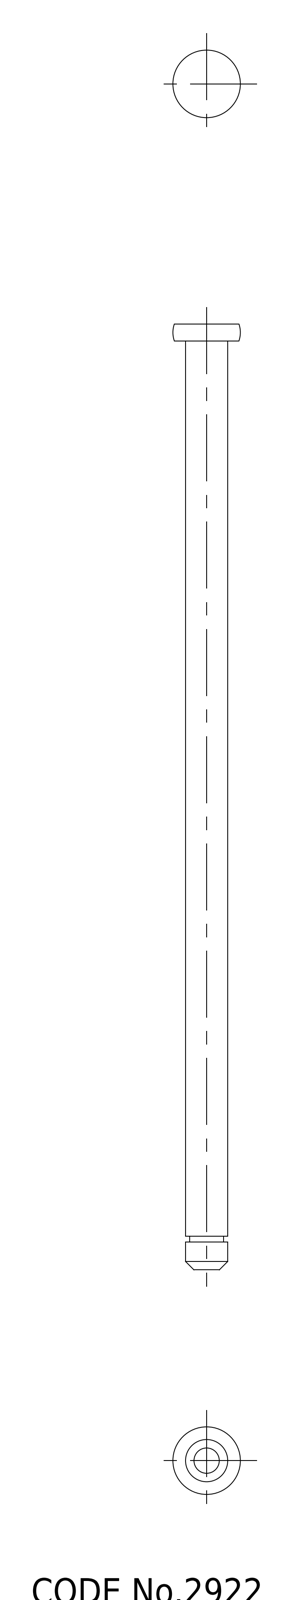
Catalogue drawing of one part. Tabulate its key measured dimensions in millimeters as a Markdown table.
| quantity | value |
| --- | --- |
| part name | TH_121SUS_5_110; shaft |
| STEP written by | SolidWorks 2015 (AUTOMOTIVE_DESIGN) |
| units | millimeters |
| bodies | 1 solid, 15 faces (5 planar, 6 cylindrical, 4 other) |
| overall size | 112 × 8 × 8 |
| volume | 2 246 mm³ |
| surface area | 1 872 mm² |
| round bosses / shafts (diameter × count) | 5 × 1, 4 × 1 |
| main face-to-face distances | 2, 0.7, 106.7, 108.7, 106, 108, 3.3, 4, 110, 112 |
